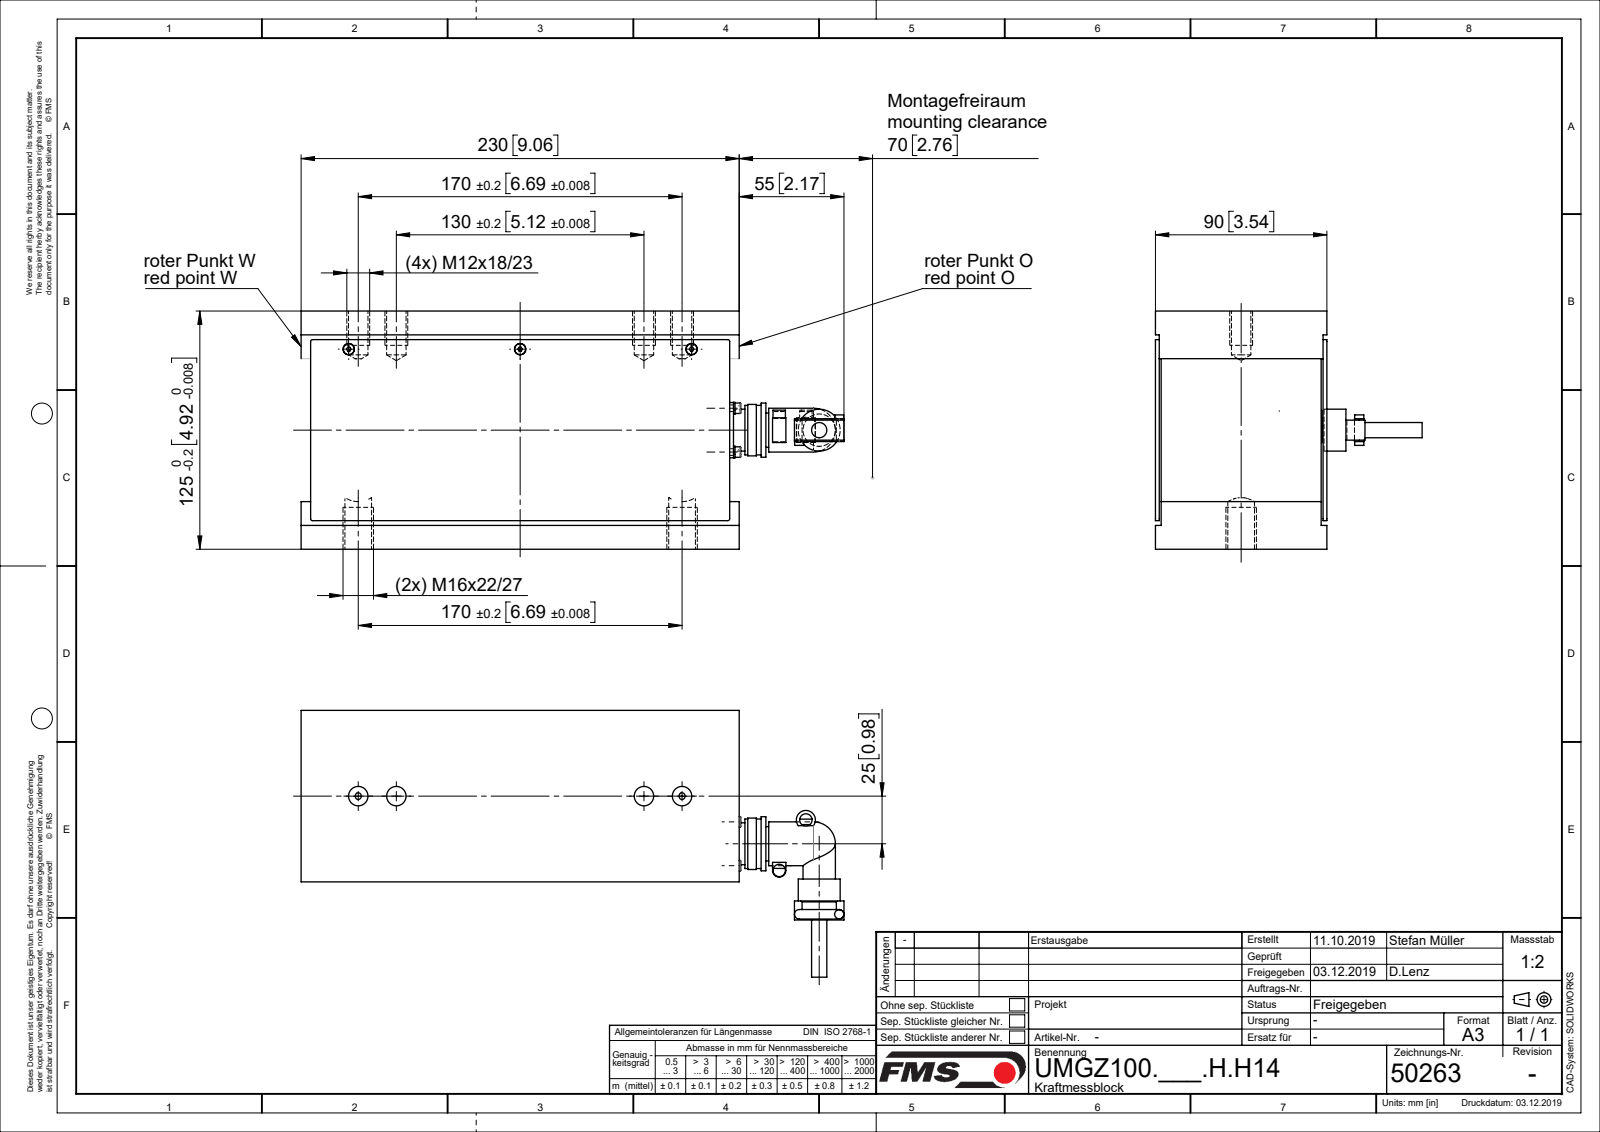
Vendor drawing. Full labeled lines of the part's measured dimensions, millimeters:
Part name (STEP PRODUCT): U50263; U4789304; U47671; TEIL1 (+5 more)
STEP written by: Mechanical Desktop 2007 (CONFIG_CONTROL_DESIGN)
Units: millimetres
Bodies: 18 solids, 408 faces (155 planar, 162 cylindrical, 91 other)
Overall size (bounding box): 285 × 125 × 90
Volume: 2 481 000 mm³ · Surface area: 231 137 mm²
Round holes (diameter × count): ⌀2.6 ×7, ⌀3.2 ×4, ⌀3.5 ×4, ⌀10.68 ×4, ⌀3.4 ×3, ⌀6 ×3, ⌀12 ×2, ⌀14.68 ×2, ⌀23 ×1
Round bosses / shafts (diameter × count): ⌀3 ×7, ⌀6.2 ×4, ⌀5.5 ×4, ⌀22 ×2, ⌀6.5 ×2, ⌀4.8 ×2, ⌀28.4 ×1, ⌀27 ×1
Partial cylindrical surfaces — rounded edges, fillets, slot ends (radius × count): R2.5 ×2, R3.5 ×1, R5 ×1
Main face-to-face distances: 2, 88, 85, 3, 87, 1, 90, 86, 125, 84
Hole centre spacings: 16.26, 23, 20, 32.53, 50, 70, 80, 90
